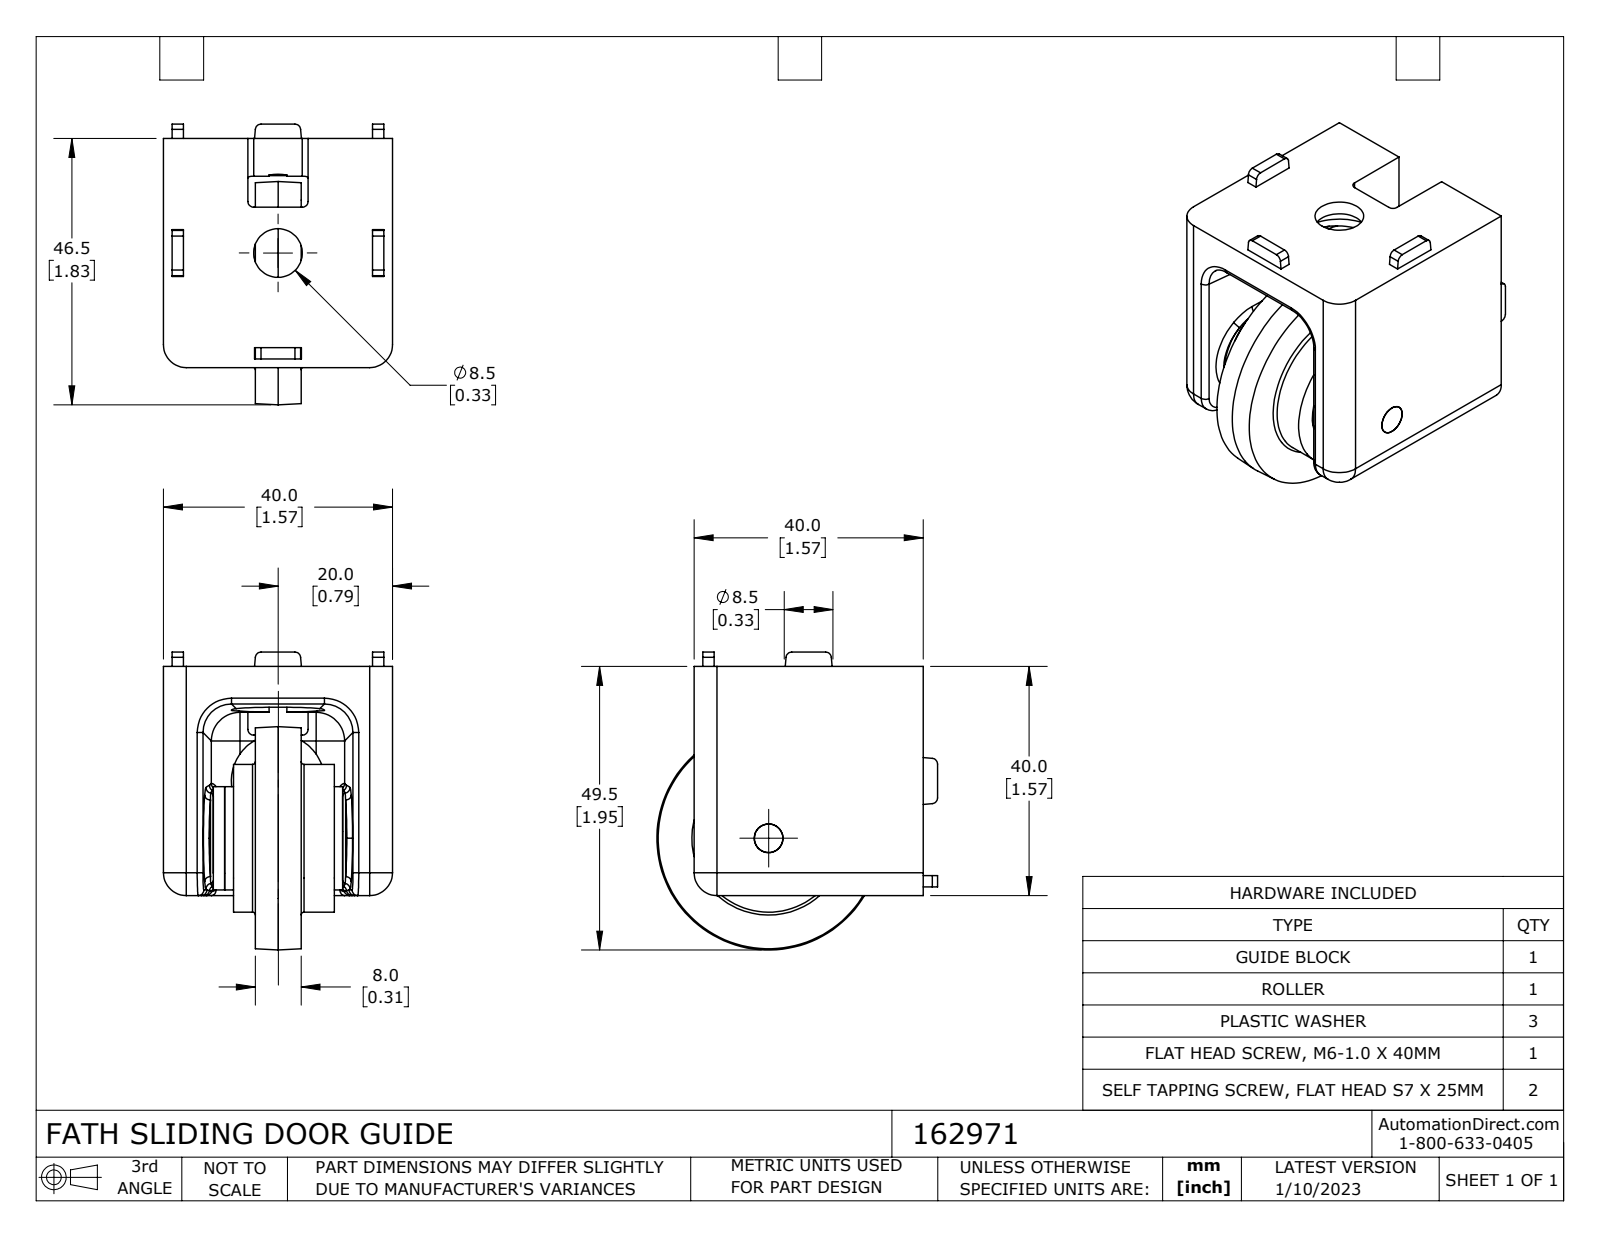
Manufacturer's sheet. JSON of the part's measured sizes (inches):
{"part_name": "162971", "step_written_by": "SolidWorks 2021 (CONFIG_CONTROL_DESIGN)", "units": "inches", "bodies": {"solids": 9, "faces": 283, "planar": 83, "cylindrical": 117, "other": 83}, "overall_size": [2.047, 1.929, 1.575], "volume_in3": 3.085, "surface_area_in2": 34.17, "round_holes": [[0.335, 2], [0.642, 2], [0.197, 1], [0.236, 1], [0.248, 1], [0.252, 1], [0.26, 1], [0.5, 1], [0.594, 1], [0.748, 1]], "round_bosses_or_shafts": [[1.016, 1], [0.709, 1], [0.472, 1], [0.39, 1]], "partial_cylinders_radius": [[0.039, 24], [0.02, 8], [0.157, 5], [0.197, 5], [0.311, 1]], "face_to_face_distances": [1.575, 0.079, 0.343, 1.232, 0.315, 0.421, 1.154, 0.811, 0.285, 0.947]}
